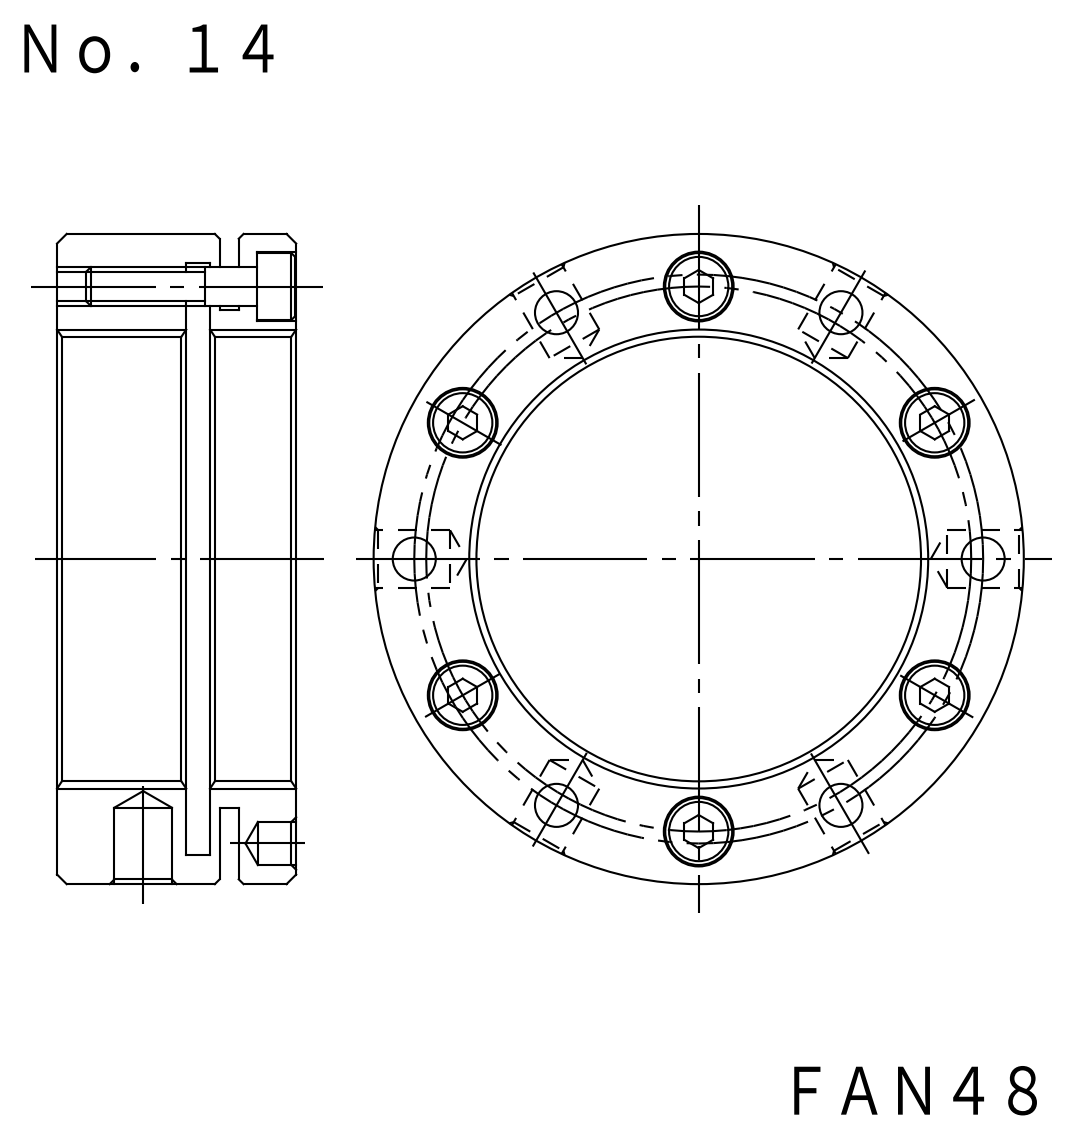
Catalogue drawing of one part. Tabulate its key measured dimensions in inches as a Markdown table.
| quantity | value |
| --- | --- |
| part name | FKD FAN48; M4X18_default |
| STEP written by | SolidWorks 2012 (CONFIG_CONTROL_DESIGN) |
| units | inches |
| bodies | 7 solids, 204 faces (72 planar, 108 cylindrical, 24 other) |
| overall size | 2.677 × 2.677 × 0.984 |
| volume | 2.316 in³ |
| surface area | 35.7 in² |
| round holes (diameter × count) | 0.128 × 6, 0.169 × 6, 0.177 × 6, 0.287 × 6, 0.236 × 3, 1.89 × 1, 2.48 × 1 |
| round bosses / shafts (diameter × count) | 0.276 × 6, 0.157 × 6, 2.677 × 1, 2.087 × 1 |
| main face-to-face distances | 0.236, 0.984, 0.157, 0.079, 0.669, 0.315, 0.748, 0.512, 0.472, 0.61 |
| hole center spacings | 1.142, 1.171, 1.636, 0.599, 2.234, 2.234, 1.635, 1.171 |
